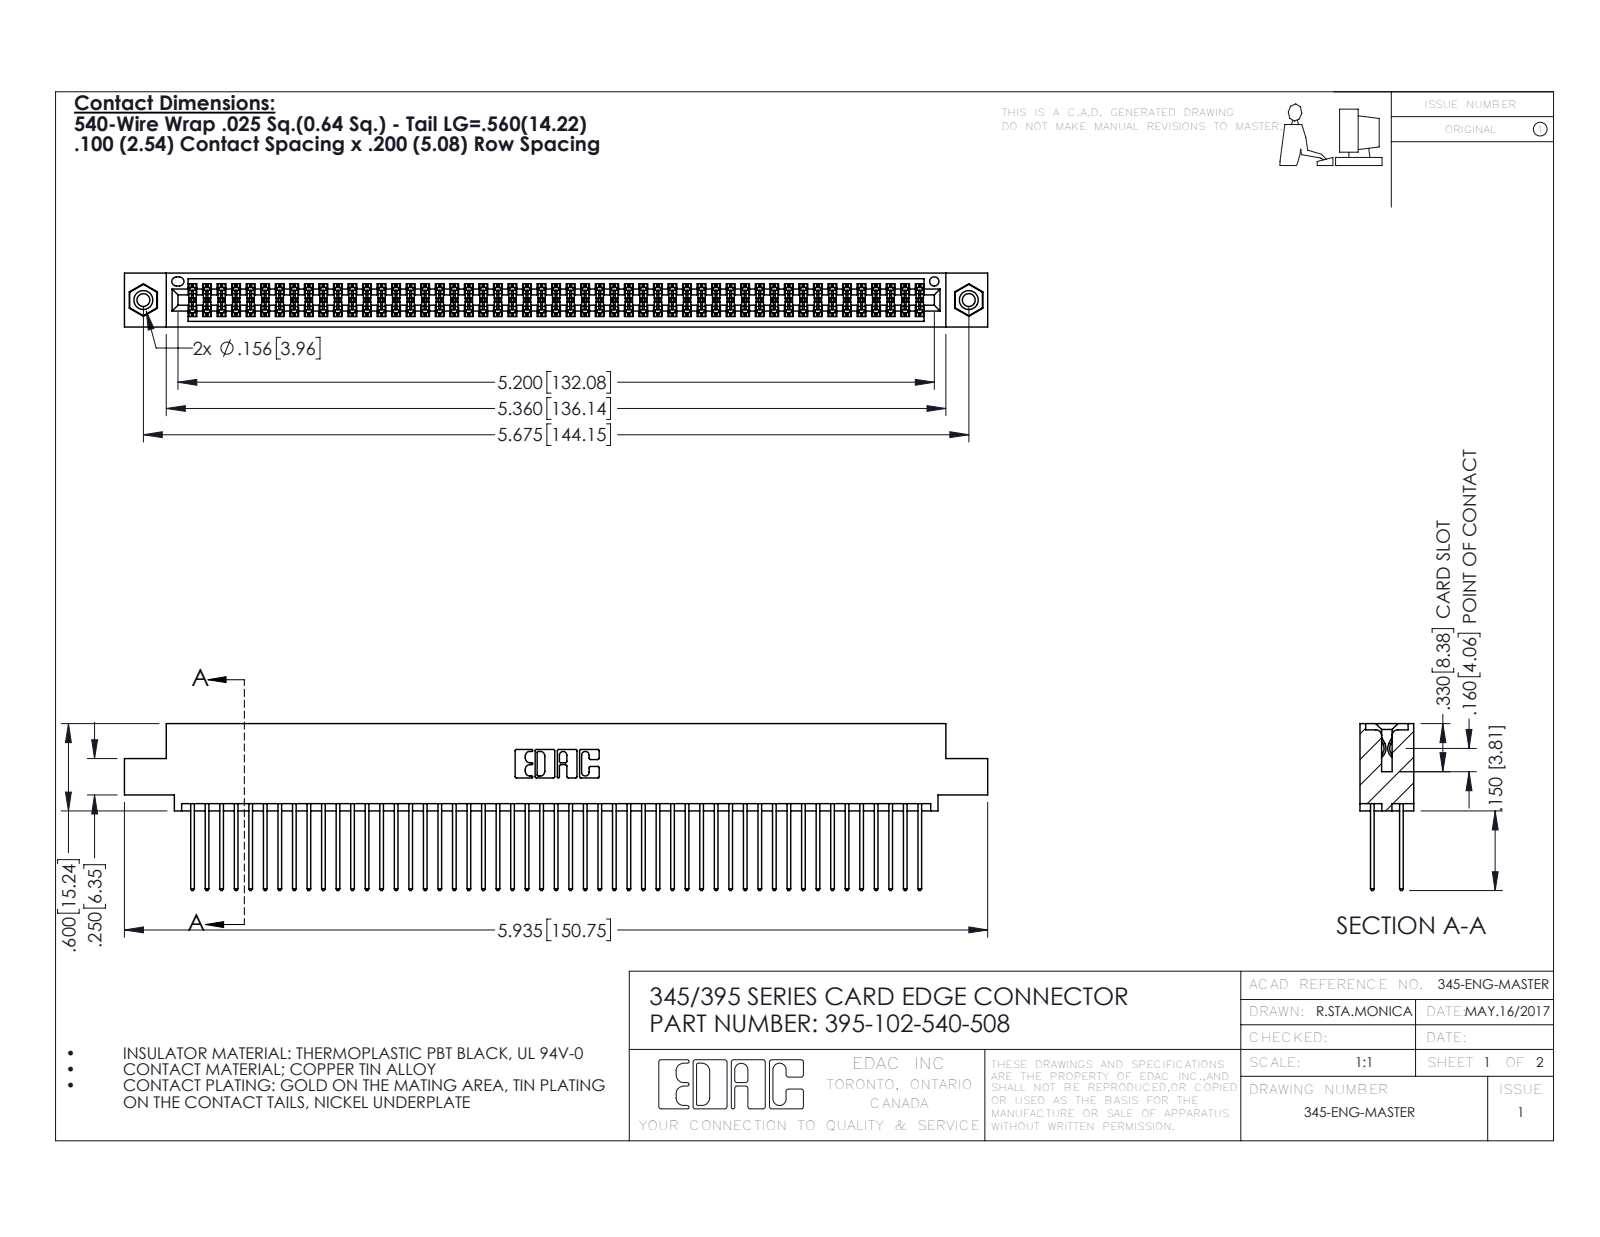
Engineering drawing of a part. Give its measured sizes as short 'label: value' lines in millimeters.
name: 345 Part_0.110 Offset - 0.156 Dia-TI; 345-292-001_345-293-140; 345-250-001_345-250-003-102; 395-102-540-508
written by: SolidWorks 2016 (CONFIG_CONTROL_DESIGN)
unit: mm
bodies: 105 solids, 5290 faces (3482 planar, 1792 cylindrical, 16 other)
size: 150.7 × 29.1 × 9.4
volume: 15 000 mm³; area: 24 300 mm²
holes: 2× ⌀2.3, 2× ⌀3.2, 2× ⌀4, 1× ⌀1.6
bosses: 2× ⌀3.9
rounds: 153× R0.2, 102× R0.3, 22× R0.3, 6× R0.2, 6× R0.8, 3× R0.7, 2× R0.4, 2× R0.5
face distances: 1.8, 7.6, 5.1, 2.5, 6.9, 0.6, 9.4, 5.7, 4.4, 3.8
hole spacings: 6.9, 138.2, 144.1
